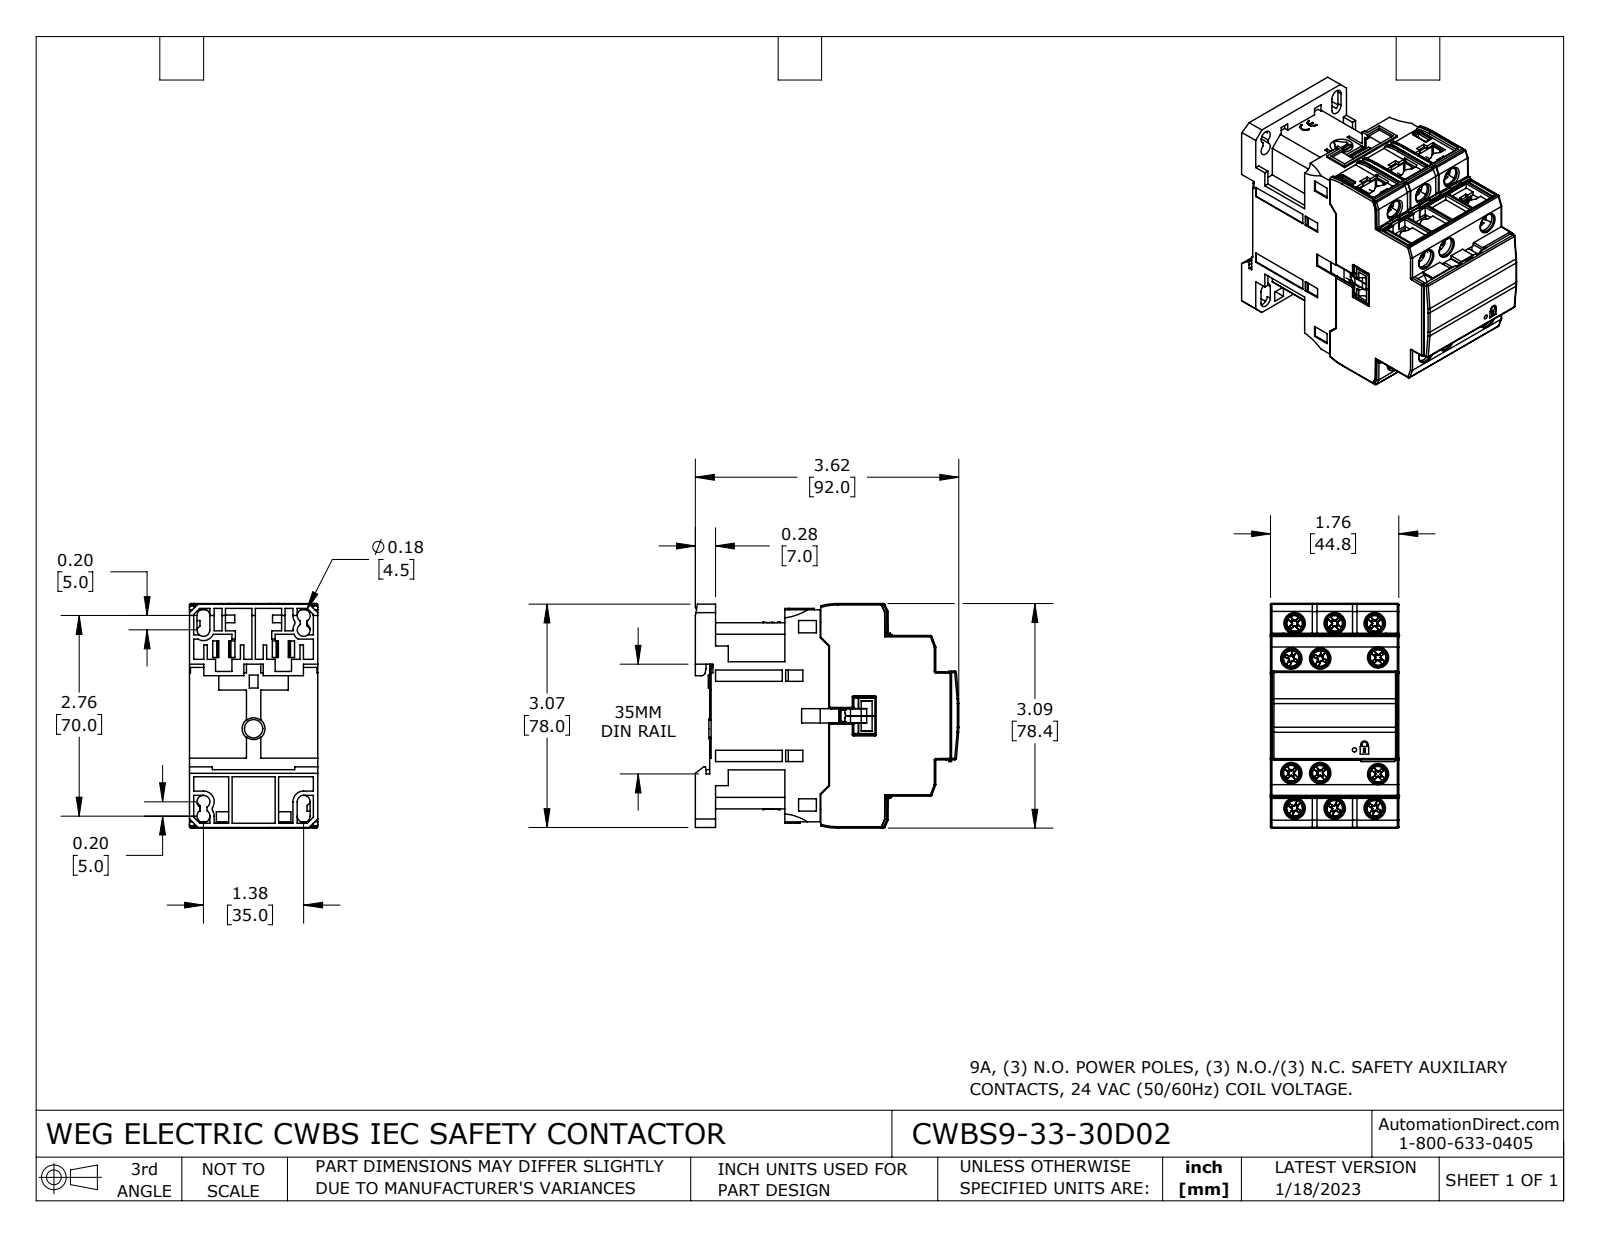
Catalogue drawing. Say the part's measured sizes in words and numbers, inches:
The part is named "CWBS9-33-30D02". Its 3-D file was written by "SolidWorks 2021 (CONFIG_CONTROL_DESIGN)". It is 45 solids with 3295 faces: 2311 planar, 624 cylindrical and 360 other. Overall it measures 3.62 by 3.087 by 1.764 inches. Its volume is 13.51 cubic inches and its surface area 120.4 square inches. Round holes: 12 of diameter 0.124, 6 of diameter 0.256, 4 of diameter 0.177, 1 of diameter 0.059. Round bosses or shafts: 12 of diameter 0.169, 12 of diameter 0.138, 8 of diameter 0.107, 4 of diameter 0.107. Partial cylindrical surfaces (rounded edges, fillets, slot ends): 139 of radius 0.02, 52 of radius 0.012, 24 of radius 0.071, 24 of radius 0.964, 24 of radius 2.128, 20 of radius 0.016, 19 of radius 0.039, 11 of radius 0.106. The main face-to-face distances are 1.764, 0.047, 1.717, 3.305, 1.754, 1.551, 0.276, 0.022, 1.776, 1.53. The hole center spacings are 0.551, 1.102, 0.197, 0.398, 0.795, 1.193, 1.341, 1.575.
